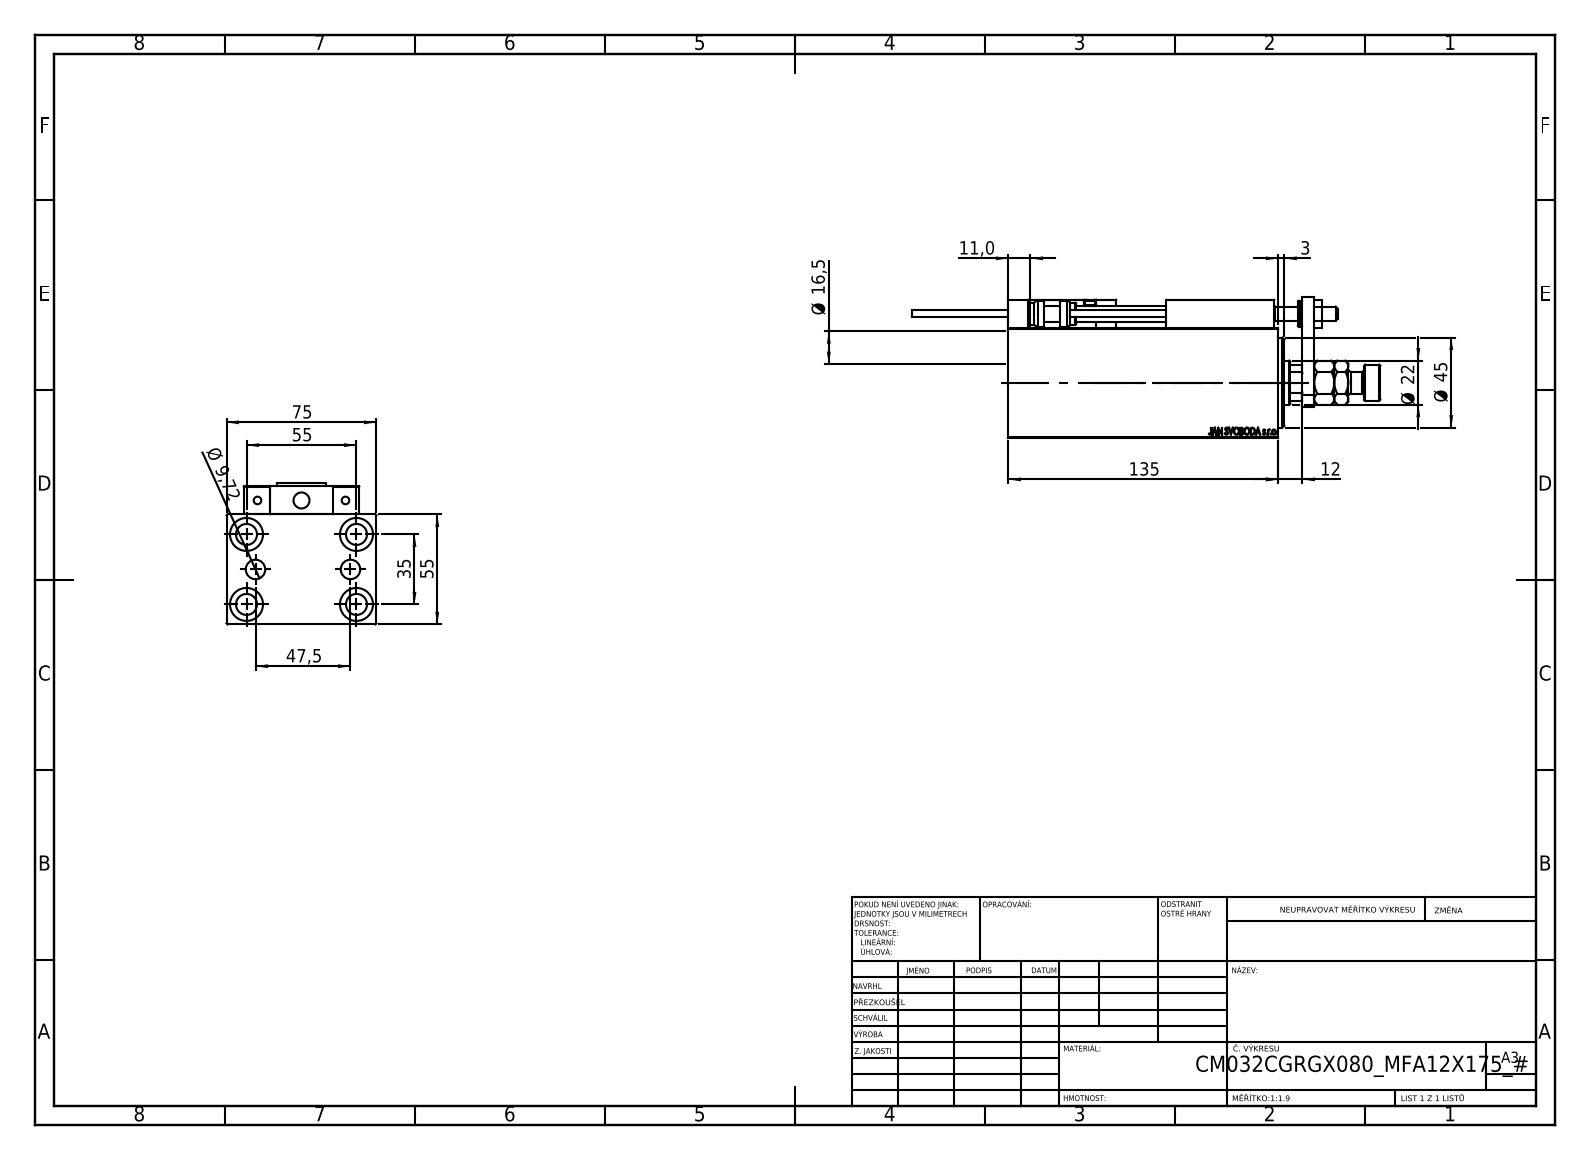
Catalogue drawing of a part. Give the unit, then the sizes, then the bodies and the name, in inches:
Units: inches
Overall size (bounding box): 9.213 × 2.953 × 2.776
Round holes (diameter × count): ⌀0.315 ×5, ⌀0.413 ×5, ⌀0.65 ×5, ⌀0.126 ×4, ⌀0.157 ×4, ⌀0.197 ×2, ⌀0.383 ×2, ⌀0.276 ×1, ⌀0.866 ×1, ⌀1.004 ×1, ⌀1.26 ×1, ⌀1.339 ×1
Round bosses / shafts (diameter × count): ⌀0.433 ×2, ⌀0.197 ×2, ⌀0.15 ×2, ⌀0.709 ×1, ⌀0.512 ×1
Partial cylindrical surfaces — rounded edges, fillets, slot ends (radius × count): R0.012 ×30, R0.118 ×2, R0.413 ×1
Main face-to-face distances: 2.165, 2.953, 0.551, 0.394, 0.472, 2.717, 0.276, 0.118, 0.984, 0.906
Hole centre spacings: 1.283, 0.448, 0.699, 0.711, 0.787, 1.165, 1.169, 1.273
Volume: 32.21 in³ · Surface area: 188.6 in²
Bodies: 24 solids, 1324 faces (574 planar, 184 cylindrical, 566 other)
Part name (STEP PRODUCT): V450CM_C_Body; ALLEN BOLT D5; ZARAZKA; ALLEN BOLT D8 (+8 more)
STEP written by: SolidWorks 2019 (CONFIG_CONTROL_DESIGN)
